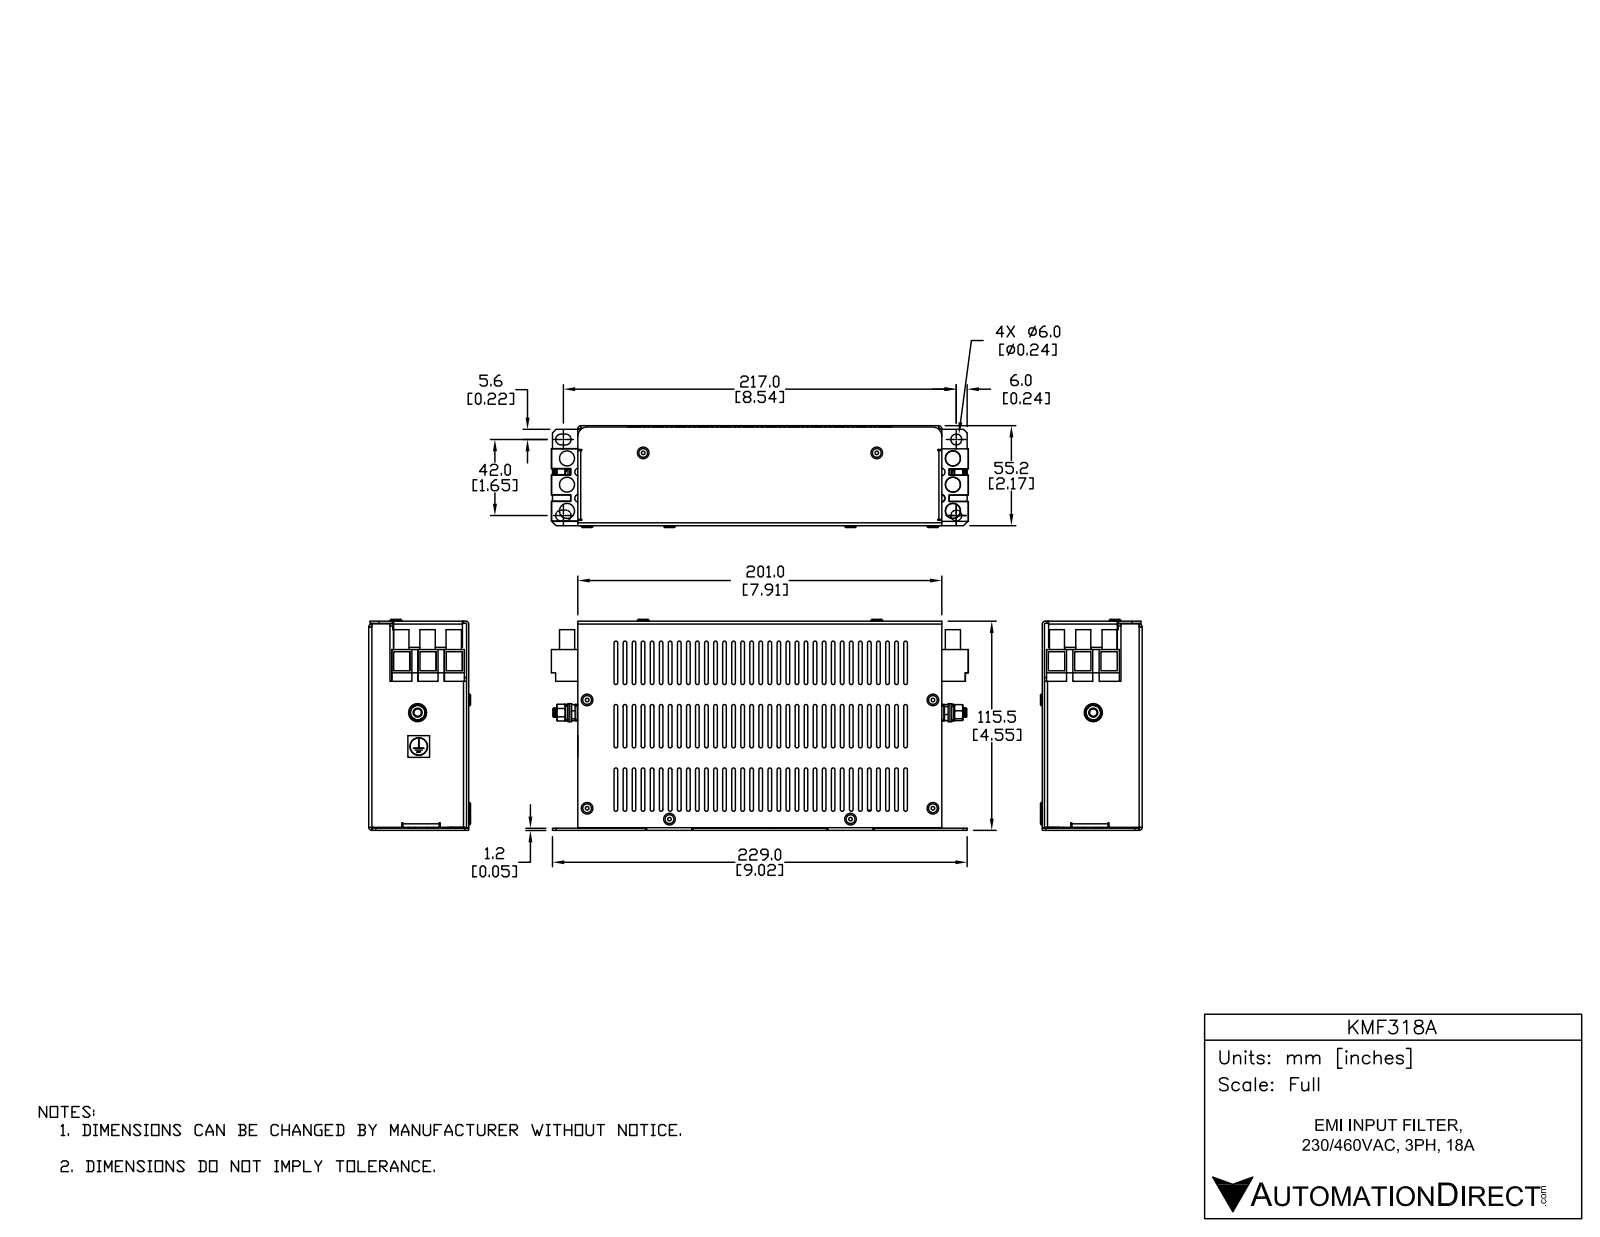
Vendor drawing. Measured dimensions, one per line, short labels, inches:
name: KMF318A
written by: SolidWorks 2017 (AUTOMOTIVE_DESIGN)
unit: in
bodies: 38 solids, 2428 faces (1384 planar, 704 cylindrical, 340 other)
size: 9.067 × 4.587 × 2.213
volume: 10.46 in³; area: 324.9 in²
holes: 12× ⌀0.079, 12× ⌀0.138, 8× ⌀0.13, 8× ⌀0.169, 2× ⌀0.154, 2× ⌀0.236, 1× ⌀0.051, 1× ⌀0.165, 1× ⌀0.165, 1× ⌀0.205, 1× ⌀0.383
bosses: 24× ⌀0.327, 12× ⌀0.138, 4× ⌀0.252, 1× ⌀0.394, 1× ⌀0.373, 1× ⌀0.315, 1× ⌀0.307, 1× ⌀0.268
rounds: 198× R0.039, 18× R0.02, 7× R0.076, 6× R0.067, 4× R0.118, 3× R0.016, 3× R0.029, 3× R0.063
face distances: 0.047, 2.126, 2.079, 4.5, 2.173, 4.547, 4.453, 7.866, 0.571, 0.059
hole spacings: 0.394, 2.354, 0.571, 1.224, 1.389, 1.807, 3.15, 5.733
